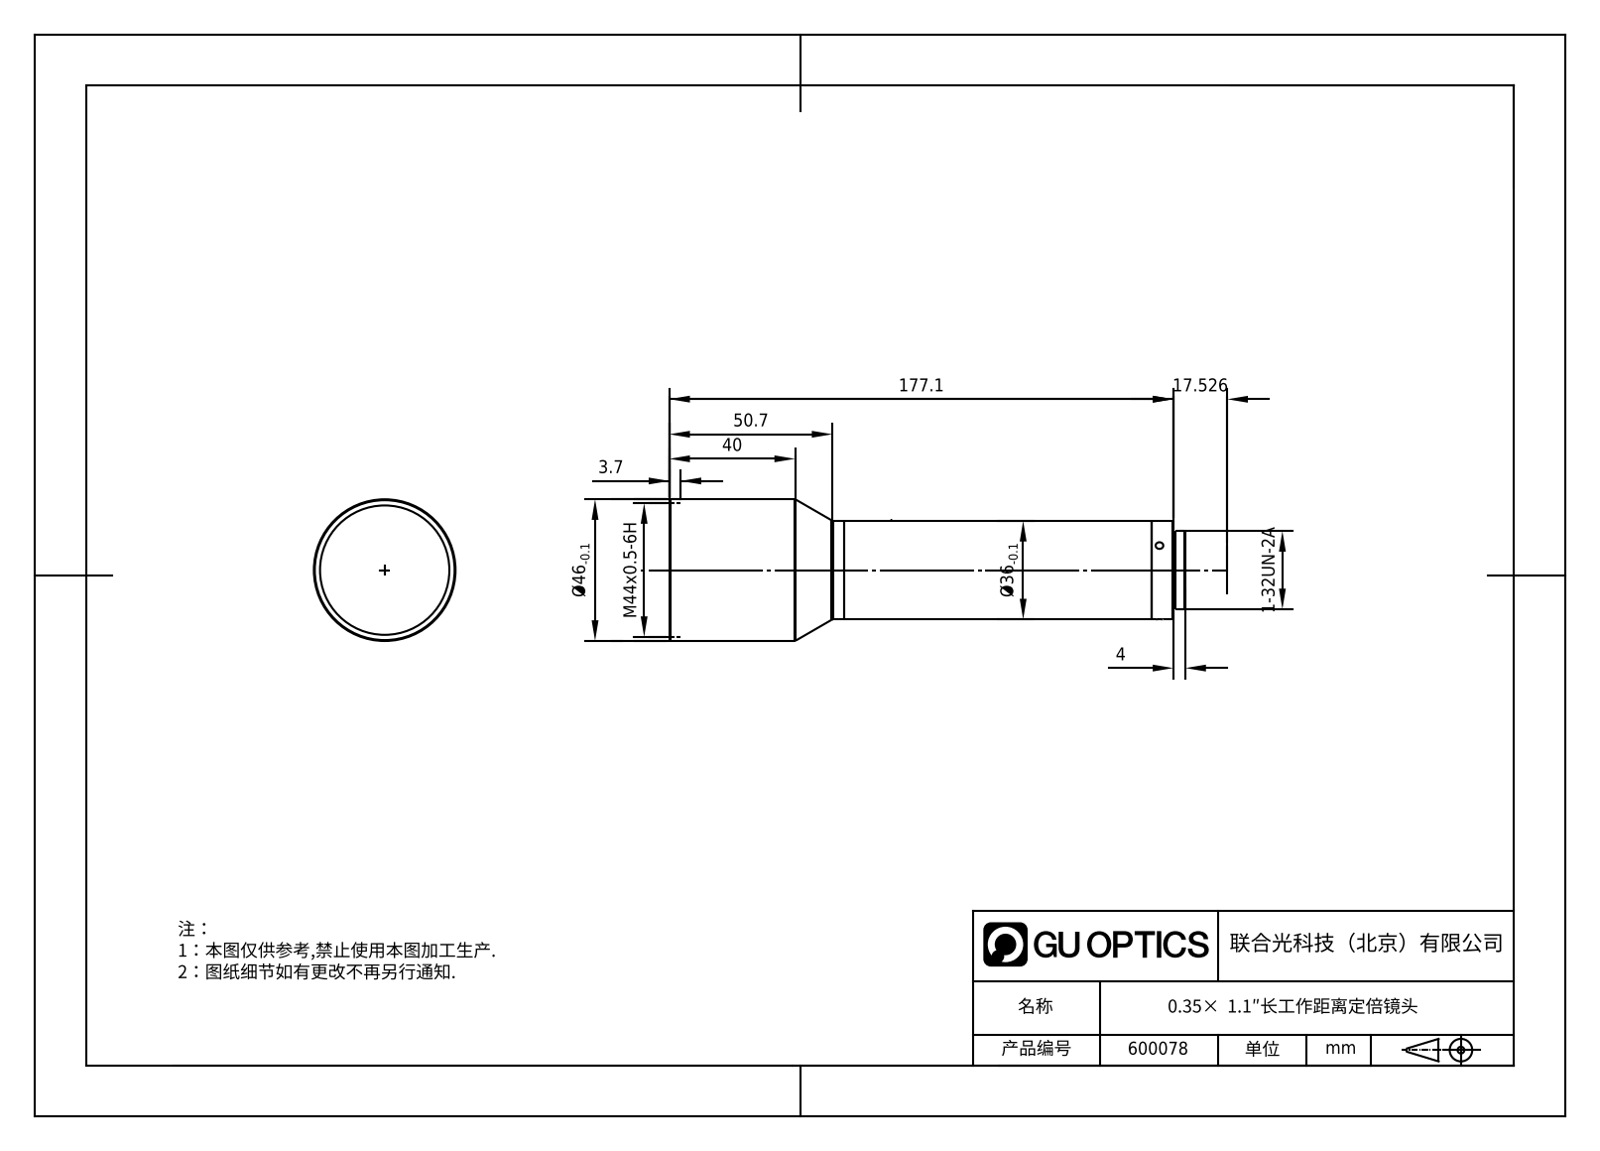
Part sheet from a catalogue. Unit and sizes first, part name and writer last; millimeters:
Units: millimetres
Overall size (bounding box): 181.08 × 46 × 46
Round holes (diameter × count): ⌀2.5 ×3, ⌀42 ×1
Round bosses / shafts (diameter × count): ⌀46 ×1, ⌀36 ×1, ⌀25.4 ×1, ⌀24.6 ×1
Partial cylindrical surfaces — rounded edges, fillets, slot ends (radius × count): R16.95 ×1
Main face-to-face distances: 168.08, 4, 172.08, 181.08, 177.08, 9, 14, 10, 158.08, 167.08
Volume: 205 311 mm³ · Surface area: 28 961 mm²
Bodies: 2 solids, 27 faces (7 planar, 12 cylindrical, 8 other)
Part name (STEP PRODUCT): 600078
STEP written by: SolidWorks 2020 (CONFIG_CONTROL_DESIGN)
